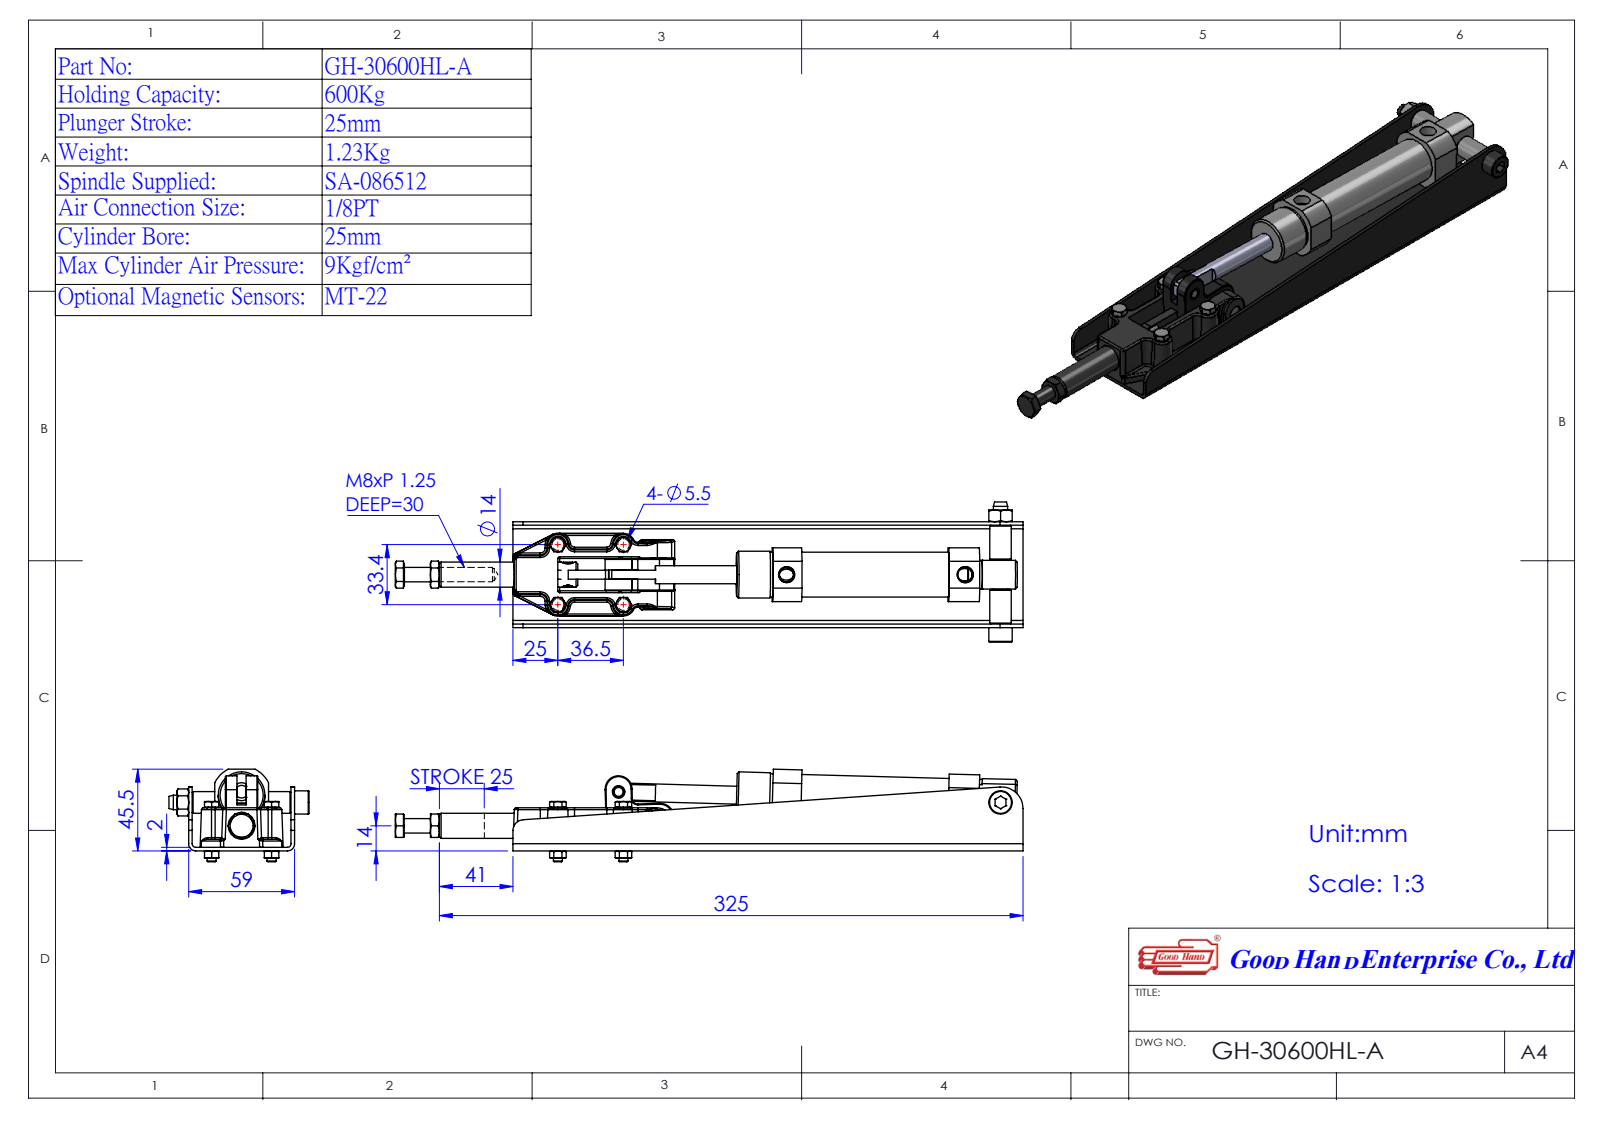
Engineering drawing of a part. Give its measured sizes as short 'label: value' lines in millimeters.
name: Group7^GH-30600HL-A(簡化)-1; Group3^GH-30600HL-A(簡化)-1; 43060005-1^GH-30600HL-A(簡化)-1; GH-30600HL-A(簡化)-1 (+4 more)
written by: SolidWorks 2016 (AUTOMOTIVE_DESIGN)
unit: mm
bodies: 7 solids, 745 faces (307 planar, 187 cylindrical, 251 other)
size: 365.3 × 73.5 × 52.22
volume: 187 975 mm³; area: 117 198 mm²
holes: 3× ⌀5, 2× ⌀6, 2× ⌀7.9, 1× ⌀6.8, 1× ⌀10, 1× ⌀12, 1× ⌀13.95, 1× ⌀15, 1× ⌀18, 1× ⌀23
bosses: 5× ⌀8, 4× ⌀5, 2× ⌀25, 2× ⌀13, 1× ⌀26, 1× ⌀14.97, 1× ⌀10
rounds: 35× R1, 6× R2, 3× R7.5, 2× R4, 2× R5, 2× R8, 2× R16.75, 1× R3
face distances: 2, 57, 55, 59, 12.5, 25, 17.5, 18.5, 1, 30
hole spacings: 18.5, 19.73, 29.03, 31.8, 35.5, 50.29, 99.49, 191.04
